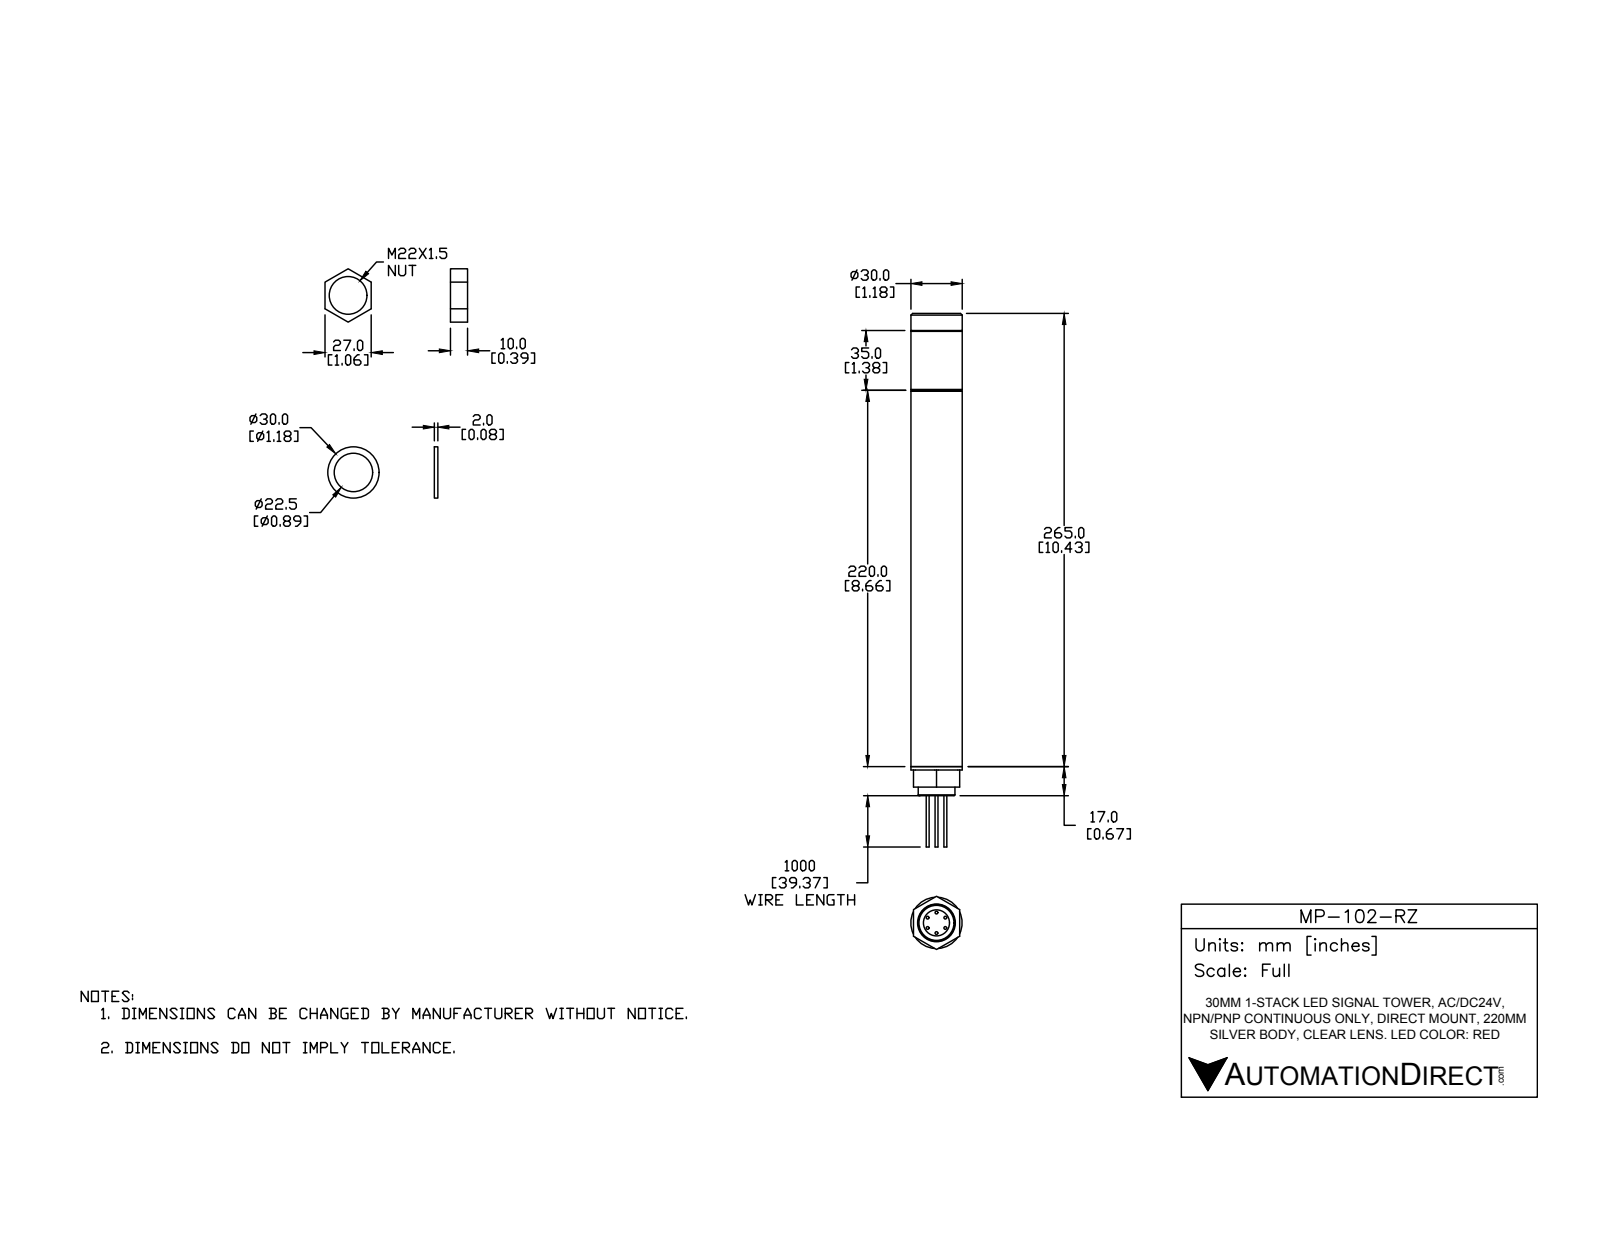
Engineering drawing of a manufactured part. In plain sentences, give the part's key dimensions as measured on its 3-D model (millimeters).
The part is named "MP-102-RZ". Its 3-D file was written by "SolidWorks 2016 (AUTOMOTIVE_DESIGN)". It is 12 solids with 95 faces: 47 planar, 36 cylindrical and 12 other. Overall it measures 312 by 31.18 by 30 millimeters. Its volume is 183 274 cubic millimeters and its surface area 39 388 square millimeters. Round holes: 1 of diameter 3.2, 1 of diameter 7.7, 1 of diameter 15.3, 1 of diameter 20.7, 1 of diameter 22. Round bosses or shafts: 6 of diameter 1.7, 1 of diameter 30, 1 of diameter 21.5, 1 of diameter 5. The main face-to-face distances are 35, 222, 45, 267, 220, 255, 10, 232, 2, 257.
